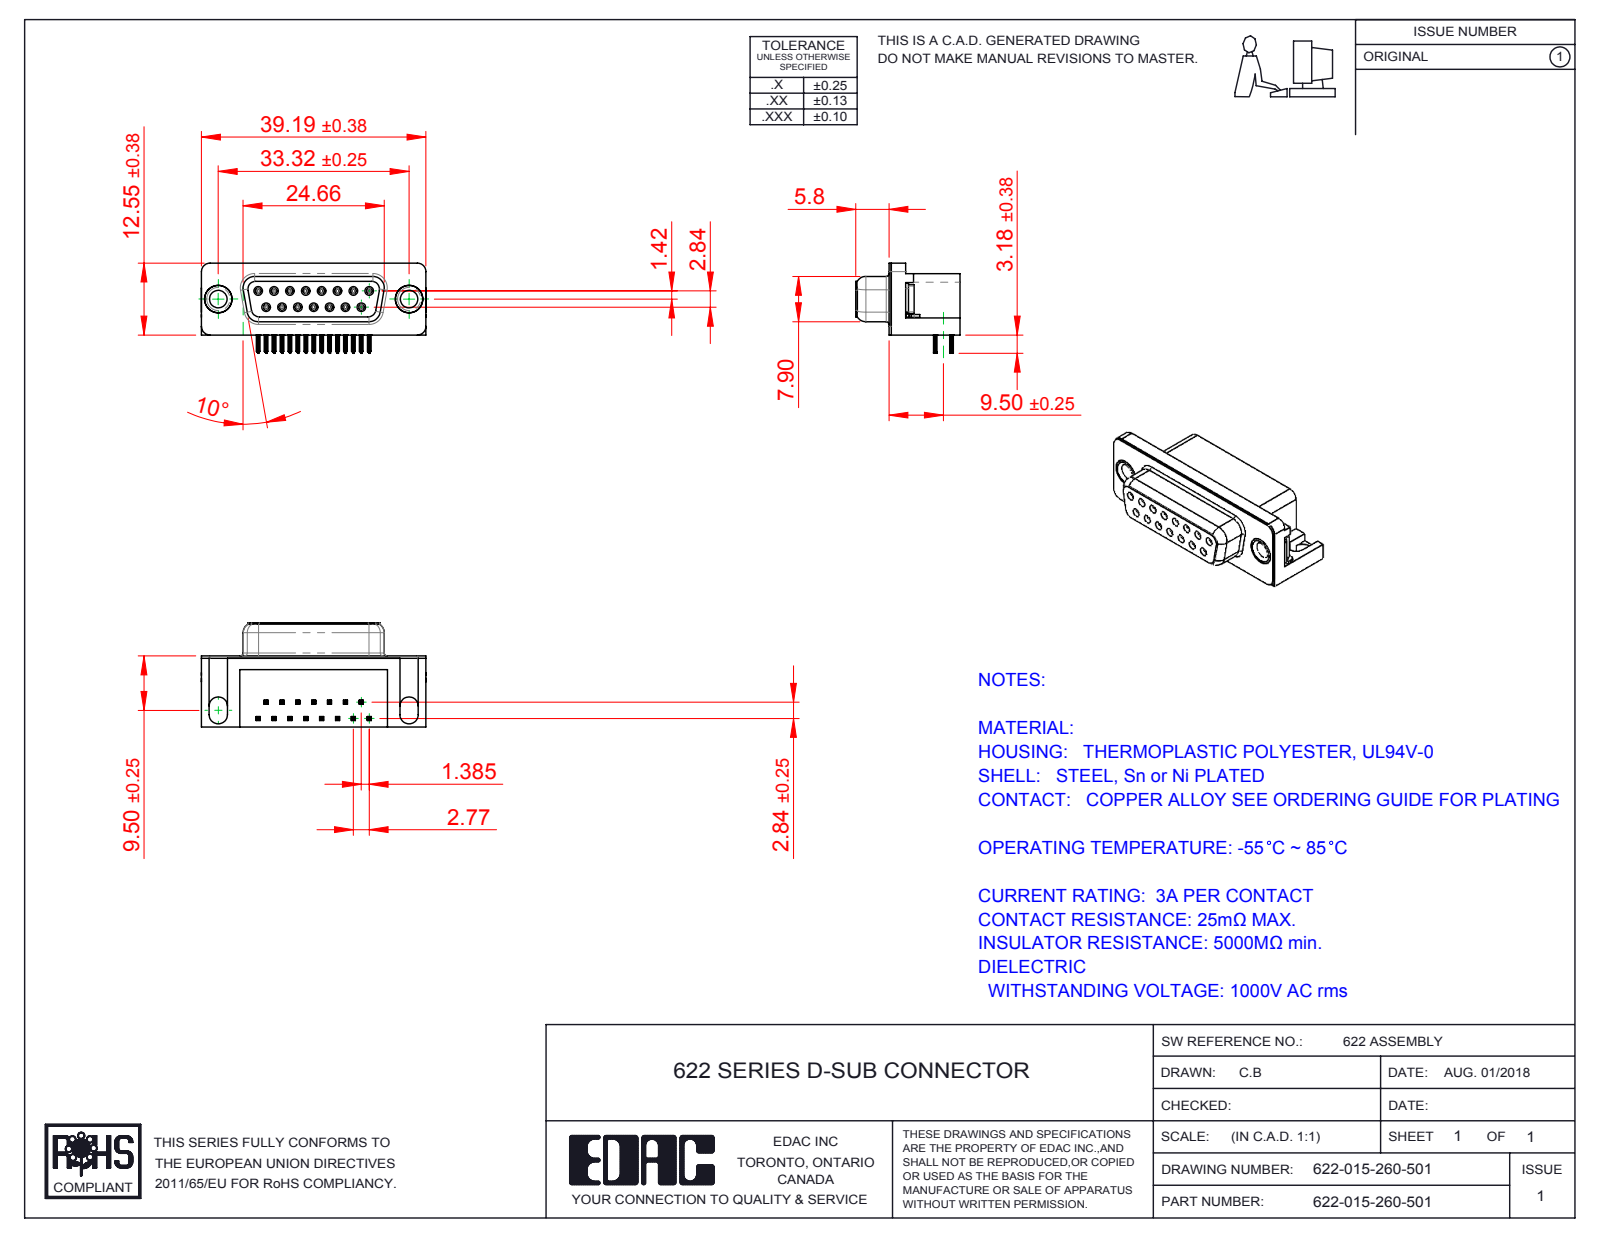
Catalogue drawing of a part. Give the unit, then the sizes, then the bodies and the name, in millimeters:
Units: millimetres
Overall size (bounding box): 39.22 × 18.2 × 15.73
Round holes (diameter × count): ⌀0.8 ×15, ⌀0.9 ×15, ⌀3.05 ×2, ⌀4 ×2, ⌀4.8 ×2, ⌀5 ×2
Round bosses / shafts (diameter × count): ⌀1.2 ×15, ⌀4.9 ×2, ⌀4.75 ×2, ⌀3.85 ×2
Partial cylindrical surfaces — rounded edges, fillets, slot ends (radius × count): R0.1 ×120, R0.15 ×60, R0.35 ×30, R1 ×18, R0.34 ×15, R0.25 ×8, R1.35 ×8, R1.5 ×8
Main face-to-face distances: 0.4, 12, 6.2, 12.4, 10.35, 2.9, 9.5, 2.5, 0.35, 0.45
Hole centre spacings: 3.16, 2.77, 5.54, 8.31, 11.08, 5.03, 5.04, 7.48
Volume: 5 140 mm³ · Surface area: 6 520 mm²
Bodies: 21 solids, 2383 faces (1074 planar, 583 cylindrical, 726 other)
Part name (STEP PRODUCT): 622 Contact Top; 622 Non Board Mount; 622 Socket Bottom; 622 Shell_15 Socket (+3 more)
STEP written by: SolidWorks 2016 (CONFIG_CONTROL_DESIGN)
